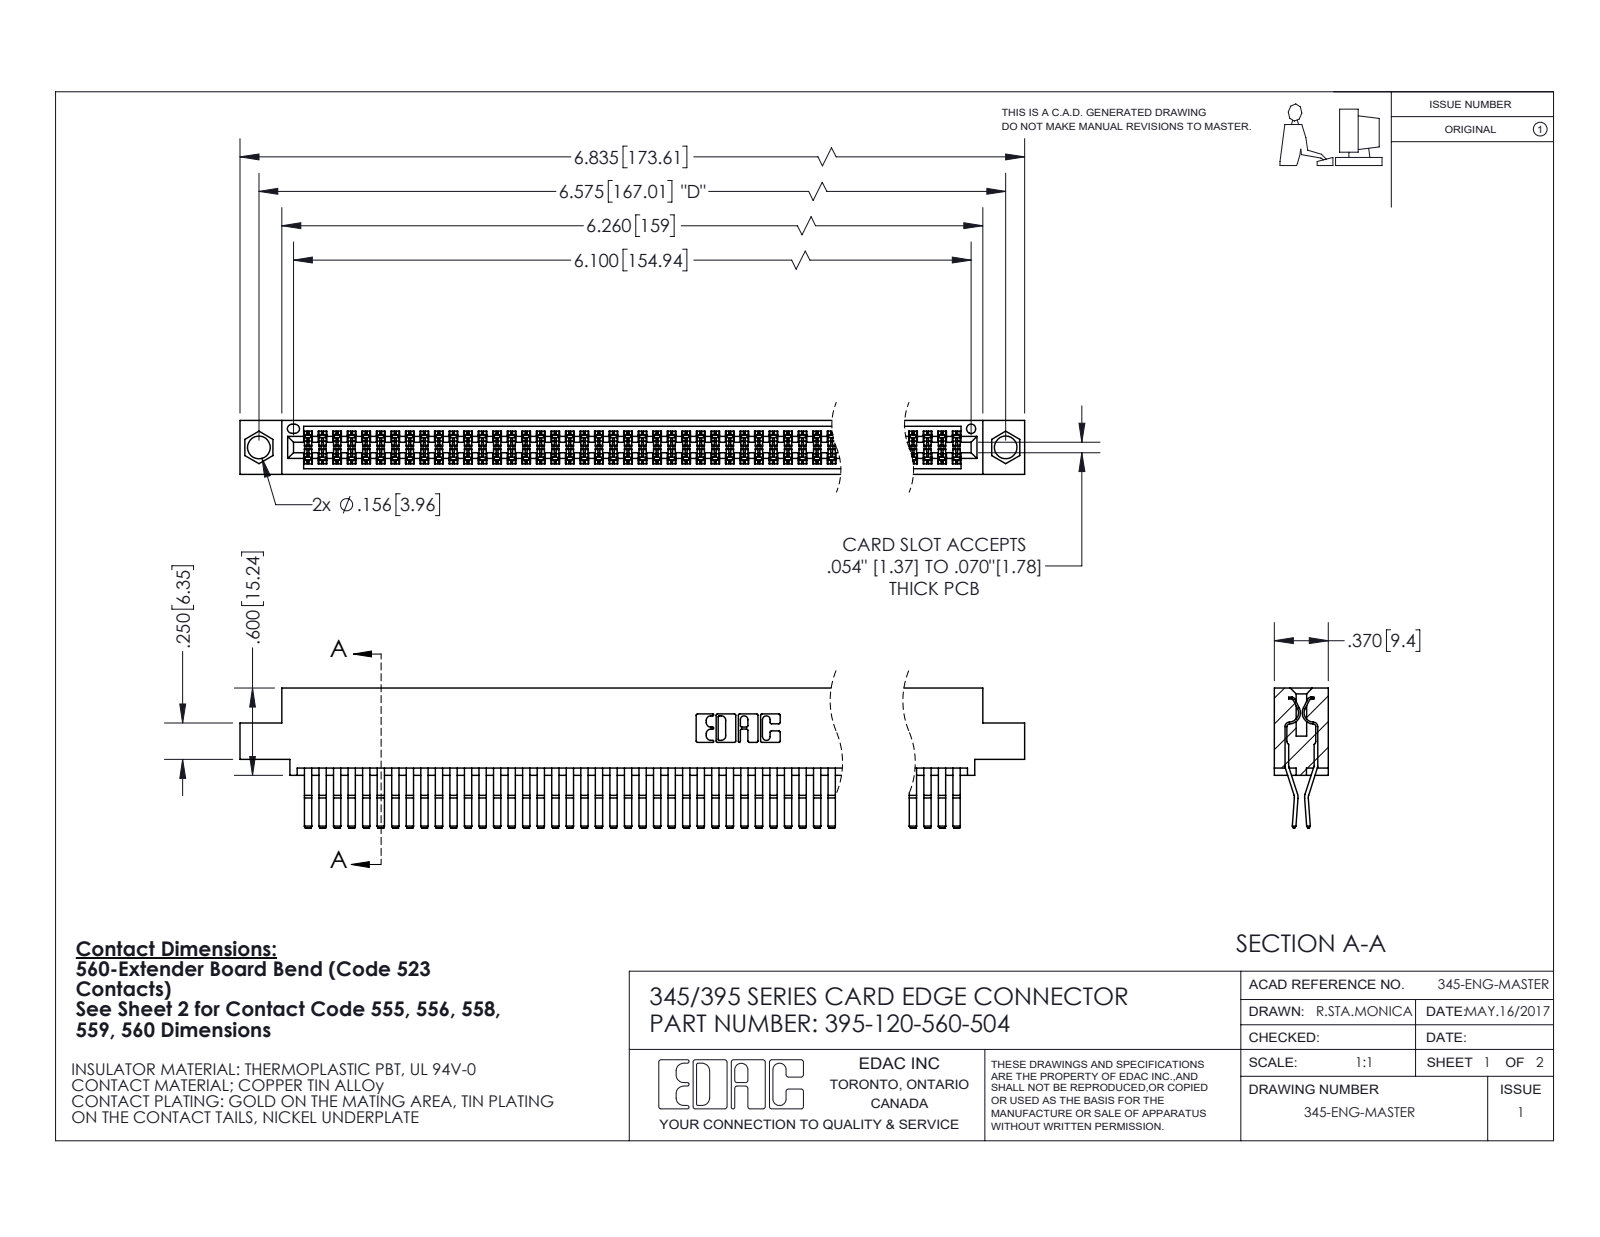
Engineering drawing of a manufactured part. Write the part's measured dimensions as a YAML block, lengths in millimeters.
part_name: "345-292-001_560 Tail; 395-120-560-504; 345 Part_0.110 Offset - 0.156 Dia-TI"
step_written_by: "SolidWorks 2020 (CONFIG_CONTROL_DESIGN)"
units: millimeters
bodies: {solids: 121, faces: 6384, planar: 4058, cylindrical: 2326, other: 0}
overall_size: [173.6, 24.4, 9.4]
volume: 17630
surface_area: 28390
round_holes:
  - {diameter: 4, count: 2}
  - {diameter: 1.6, count: 1}
partial_cylinders:
  - {radius: 0.2, count: 180}
  - {radius: 0.3, count: 22}
  - {radius: 0.2, count: 6}
  - {radius: 0.8, count: 6}
  - {radius: 0.7, count: 3}
  - {radius: 0.3, count: 2}
  - {radius: 0.4, count: 2}
  - {radius: 0.5, count: 2}
face_to_face_distances: [0.6, 7.6, 1.8, 9.4, 5.1, 2.5, 6.9, 5.7, 4.4, 3.8]
hole_center_spacings: [6.9, 161, 167]
